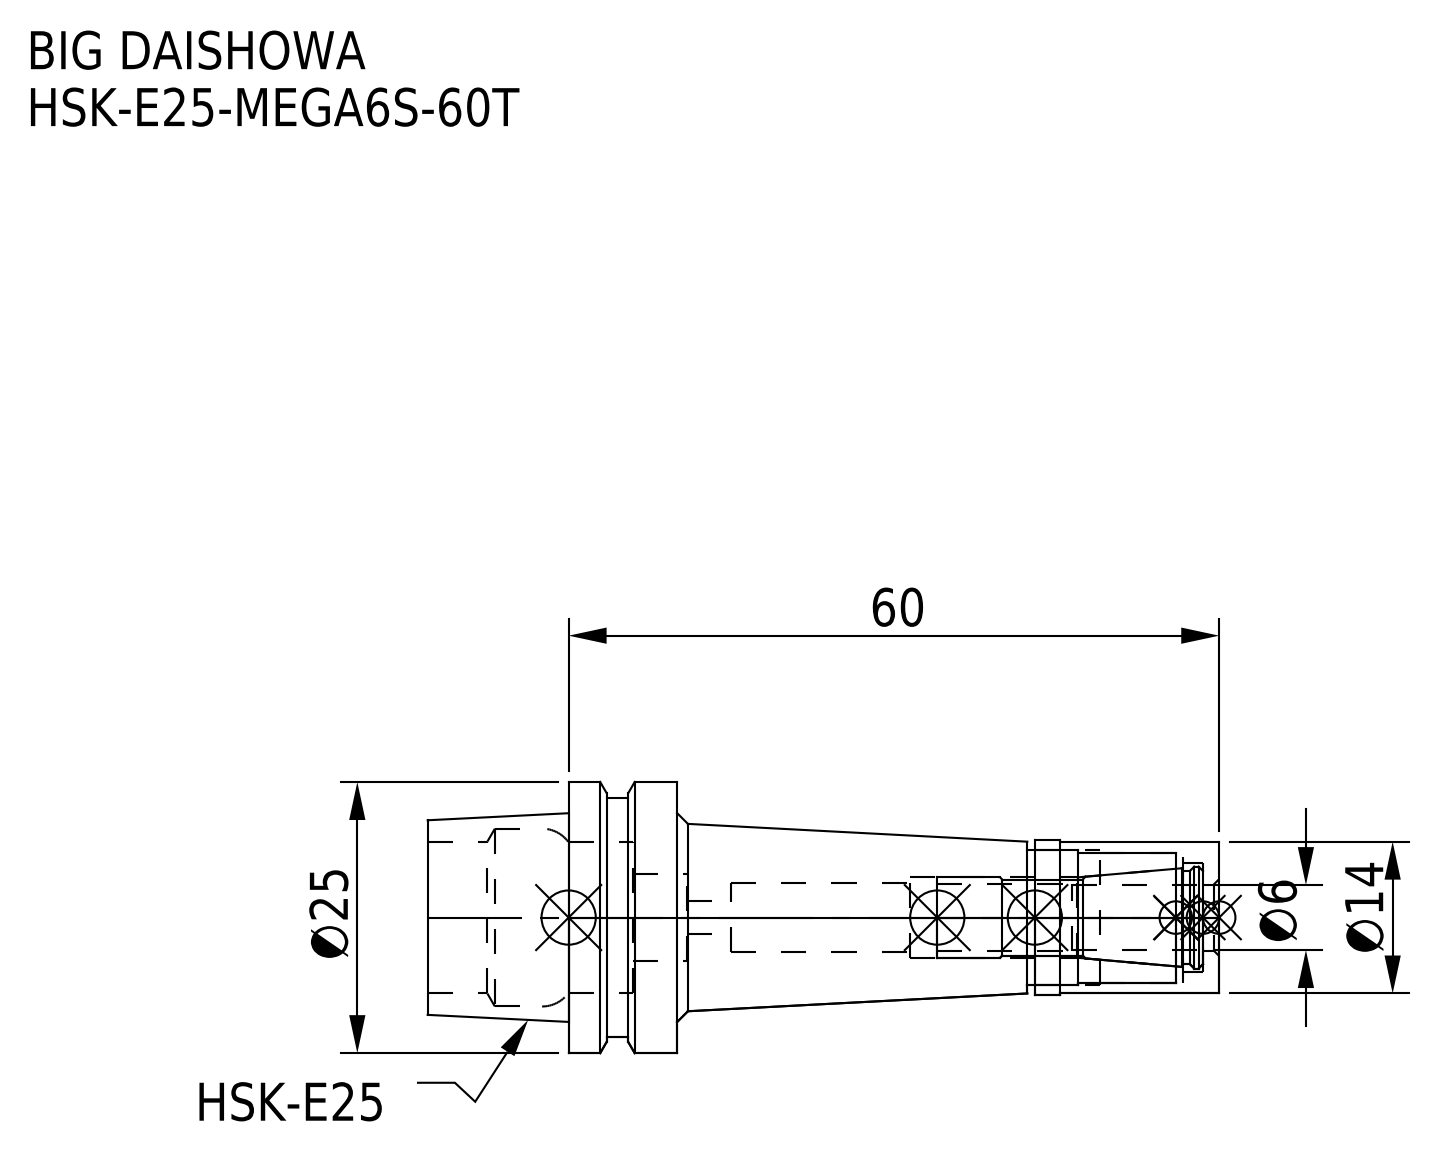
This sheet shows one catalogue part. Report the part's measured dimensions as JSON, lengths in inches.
{"part_name": "DXF_TEMP_ASSY_ASM_4_ASM.stp; HSK-E25-MEGA6S-60T-060.stp; HSK-E25-MEGA6S-60T_1.stp; HSK-E25-MEGA6S-60T (+3 more)", "step_written_by": "SolidWorks 2019 (CONFIG_CONTROL_DESIGN)", "units": "inches", "bodies": {"solids": 2, "faces": 74, "planar": 18, "cylindrical": 38, "other": 18}, "overall_size": [2.874, 0.984, 0.984], "volume_in3": 0.712, "surface_area_in2": 12.77, "round_holes": [[0.118, 1], [0.24, 1], [0.252, 1], [0.291, 1], [0.315, 1], [0.394, 1], [0.472, 1], [0.492, 1], [0.551, 1], [0.646, 1]], "round_bosses_or_shafts": [[0.984, 1], [0.866, 1], [0.563, 1]], "face_to_face_distances": [0.394, 0.512, 0.159, 2.362, 1.969, 2.128, 0.234, 2.874, 0.906, 0.746]}
